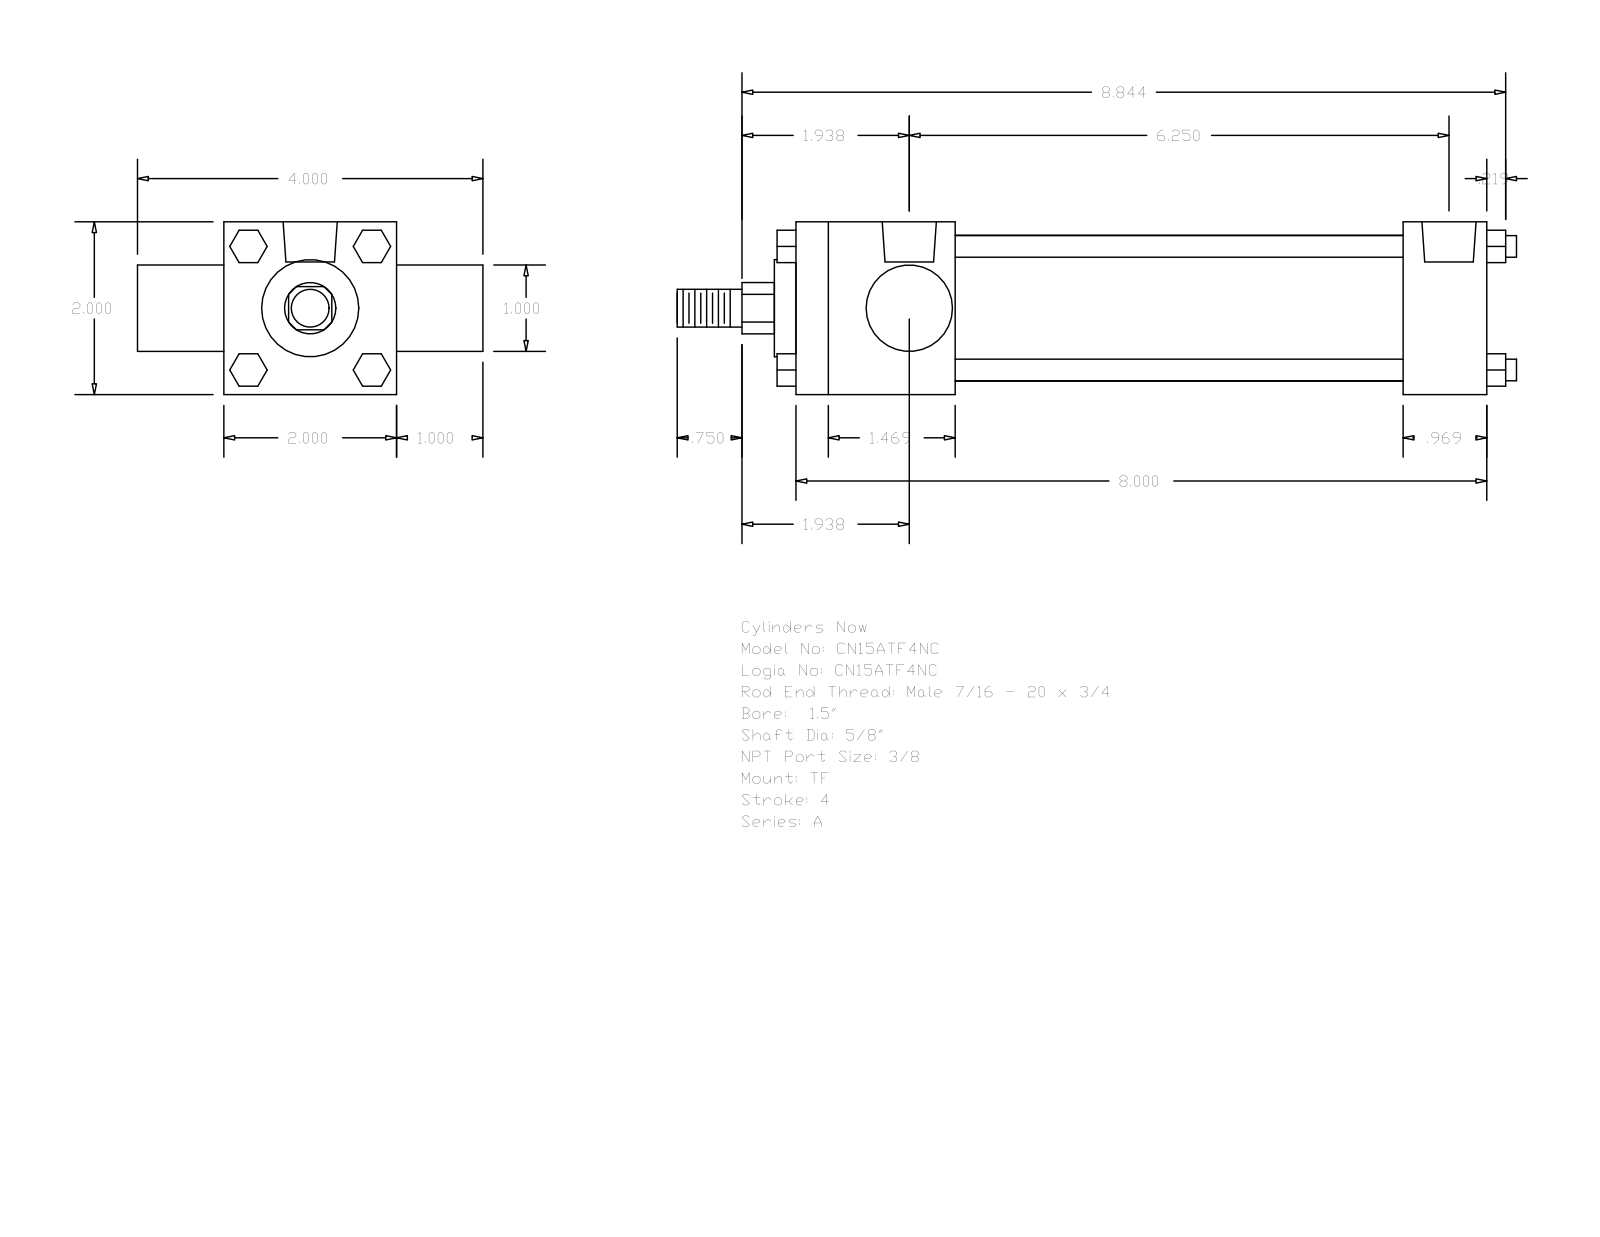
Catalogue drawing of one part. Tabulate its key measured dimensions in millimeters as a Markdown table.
| quantity | value |
| --- | --- |
| part name | A_TF__0150_0.625 |
| STEP written by | GSSL Pune (CONFIG_CONTROL_DESIGN) |
| units | millimeters |
| bodies | 0 solids, 120 faces (92 planar, 28 cylindrical, 0 other) |
| overall size | 246.86 × 101.6 × 50.8 |
| round holes (diameter × count) | 5.56 × 3, 15.93 × 2 |
| round bosses / shafts (diameter × count) | 6.35 × 4, 42.93 × 1, 28.57 × 1, 25.4 × 1, 15.88 × 1, 11.11 × 1 |
| partial cylindrical surfaces (radius × count) | 7.54 × 1 |
| main face-to-face distances | 50.8, 203.19, 25.4, 76.2, 46.83, 178.59, 131.76, 156.36, 24.6, 101.6 |
| hole center spacings | 3.97, 154.78, 150.81, 158.75 |
